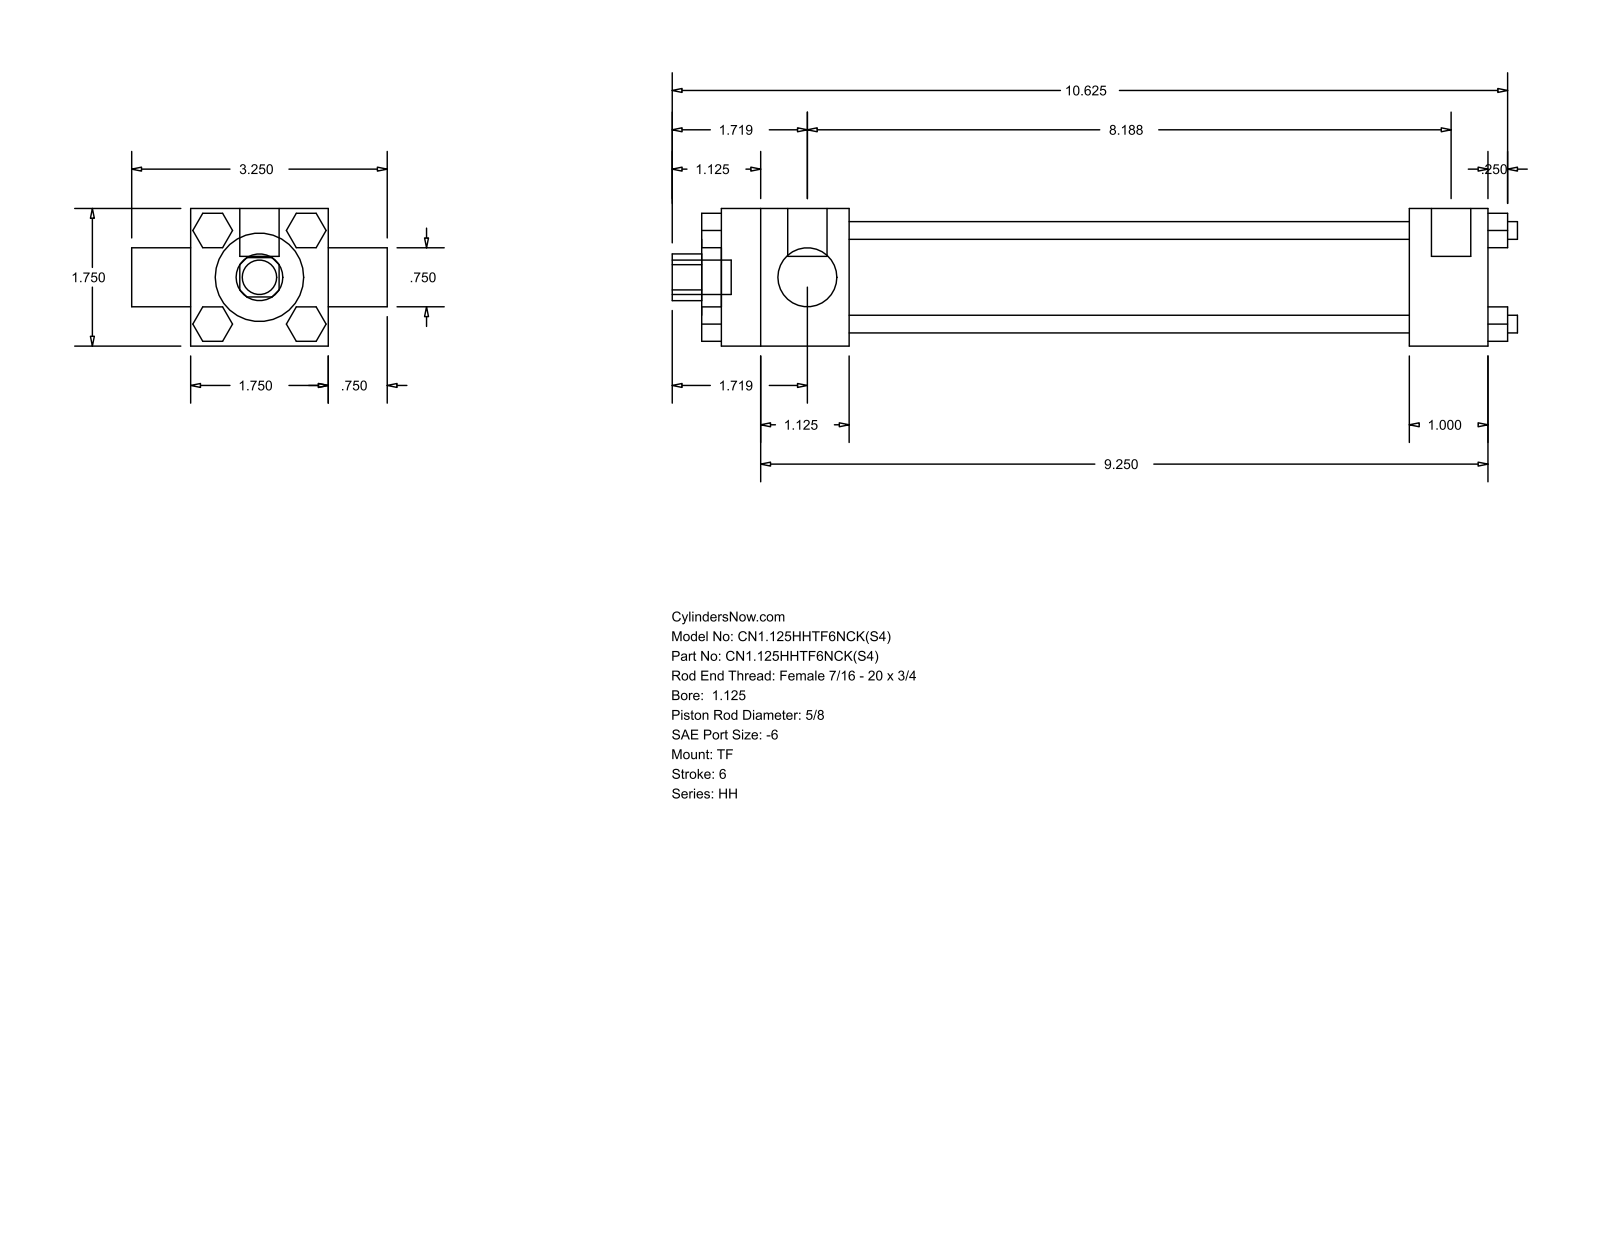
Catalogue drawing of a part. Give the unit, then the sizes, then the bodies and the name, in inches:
Units: inches
Overall size (bounding box): 10.75 × 3.25 × 1.75
Round holes (diameter × count): ⌀0.625 ×1, ⌀0.75 ×1, ⌀1.125 ×1, ⌀1.375 ×1
Round bosses / shafts (diameter × count): ⌀0.225 ×4, ⌀0.219 ×3, ⌀0.5 ×2, ⌀0.437 ×1
Partial cylindrical surfaces — rounded edges, fillets, slot ends (radius × count): R0.297 ×1
Main face-to-face distances: 1.75, 0.437, 7.125, 8.125, 1, 1.625, 8.75, 9.75, 1.875, 0.25
Bodies: 0 solids, 120 faces (92 planar, 28 cylindrical, 0 other)
Part name (STEP PRODUCT): HH_TF__0112_0.625
STEP written by: GSSL Pune (CONFIG_CONTROL_DESIGN)
